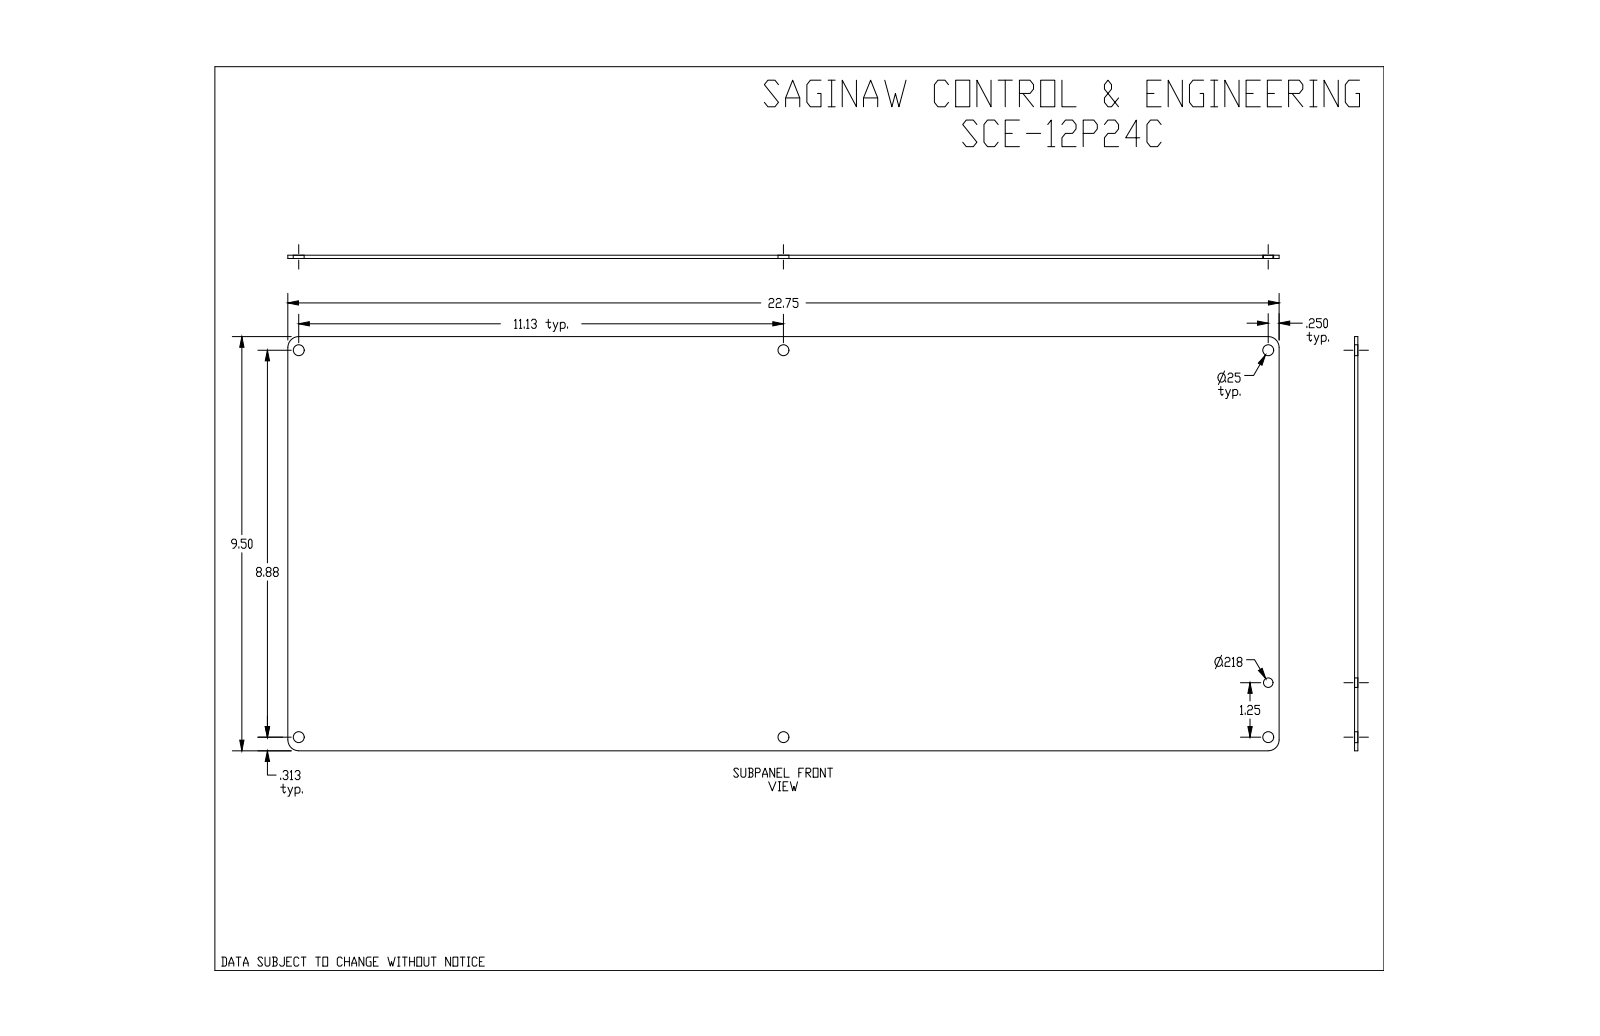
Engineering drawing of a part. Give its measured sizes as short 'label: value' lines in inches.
name: SCE-12P24C
written by: SolidWorks 2019 (CONFIG_CONTROL_DESIGN)
unit: in
bodies: 1 solid, 17 faces (6 planar, 11 cylindrical, 0 other)
size: 22.75 × 9.5 × 0.075
volume: 16.18 in³; area: 436.7 in²
holes: 6× ⌀0.25, 1× ⌀0.218
rounds: 4× R0.25
face distances: 0.075, 9.5, 22.75
hole spacings: 11.125, 14.231, 8.875, 22.25, 23.954, 1.25, 7.625, 11.195
